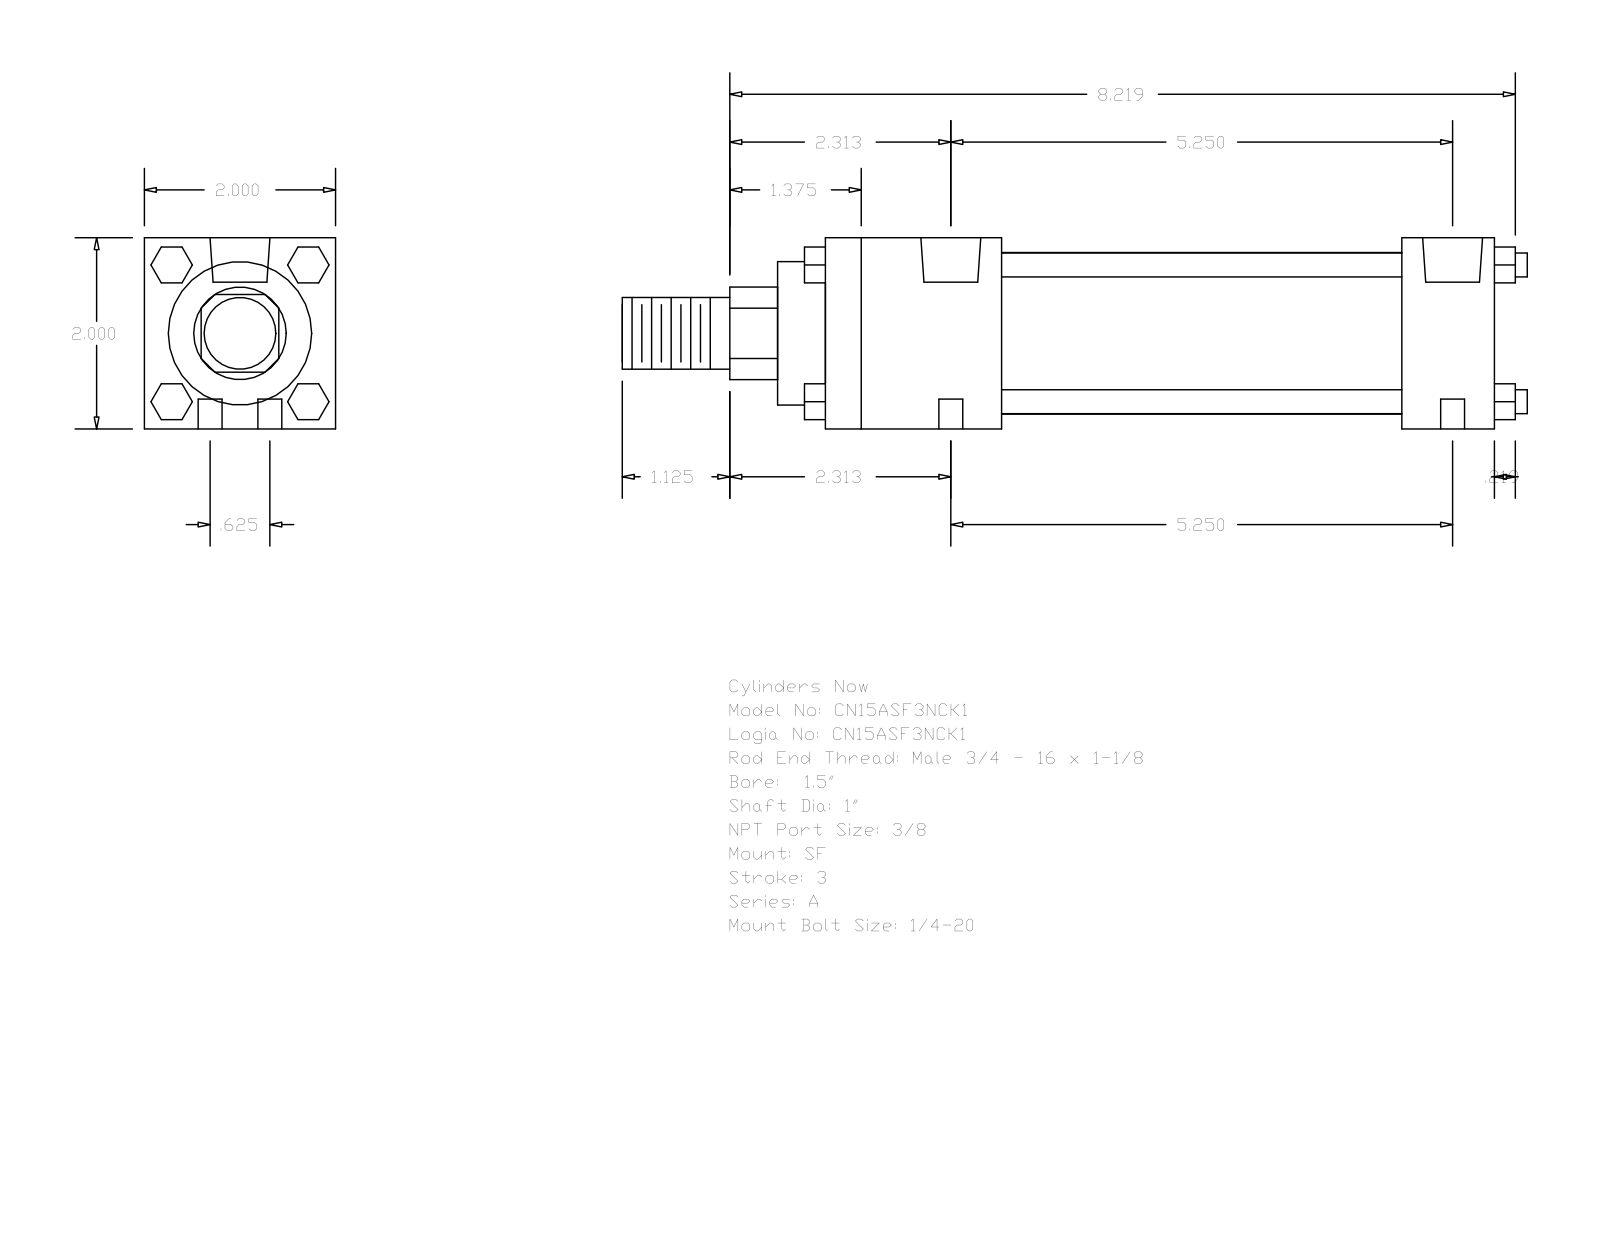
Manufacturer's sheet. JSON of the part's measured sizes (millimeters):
{"part_name": "A_SF__0150_1", "step_written_by": "GSSL Pune (CONFIG_CONTROL_DESIGN)", "units": "millimeters", "bodies": {"solids": 0, "faces": 124, "planar": 94, "cylindrical": 30, "other": 0}, "overall_size": [240.51, 50.8, 50.8], "round_holes": [[6.35, 4], [5.56, 2], [15.93, 2]], "round_bosses_or_shafts": [[6.35, 4], [42.93, 1], [38.1, 1], [25.4, 1], [19.05, 1]], "partial_cylinders_radius": [[12.29, 1]], "face_to_face_distances": [50.8, 177.8, 46.83, 153.19, 106.36, 130.97, 24.61, 12.7, 59.53, 165.89], "hole_center_spacings": [7.94, 133.59, 133.35, 15.88, 134.29, 125.41]}
